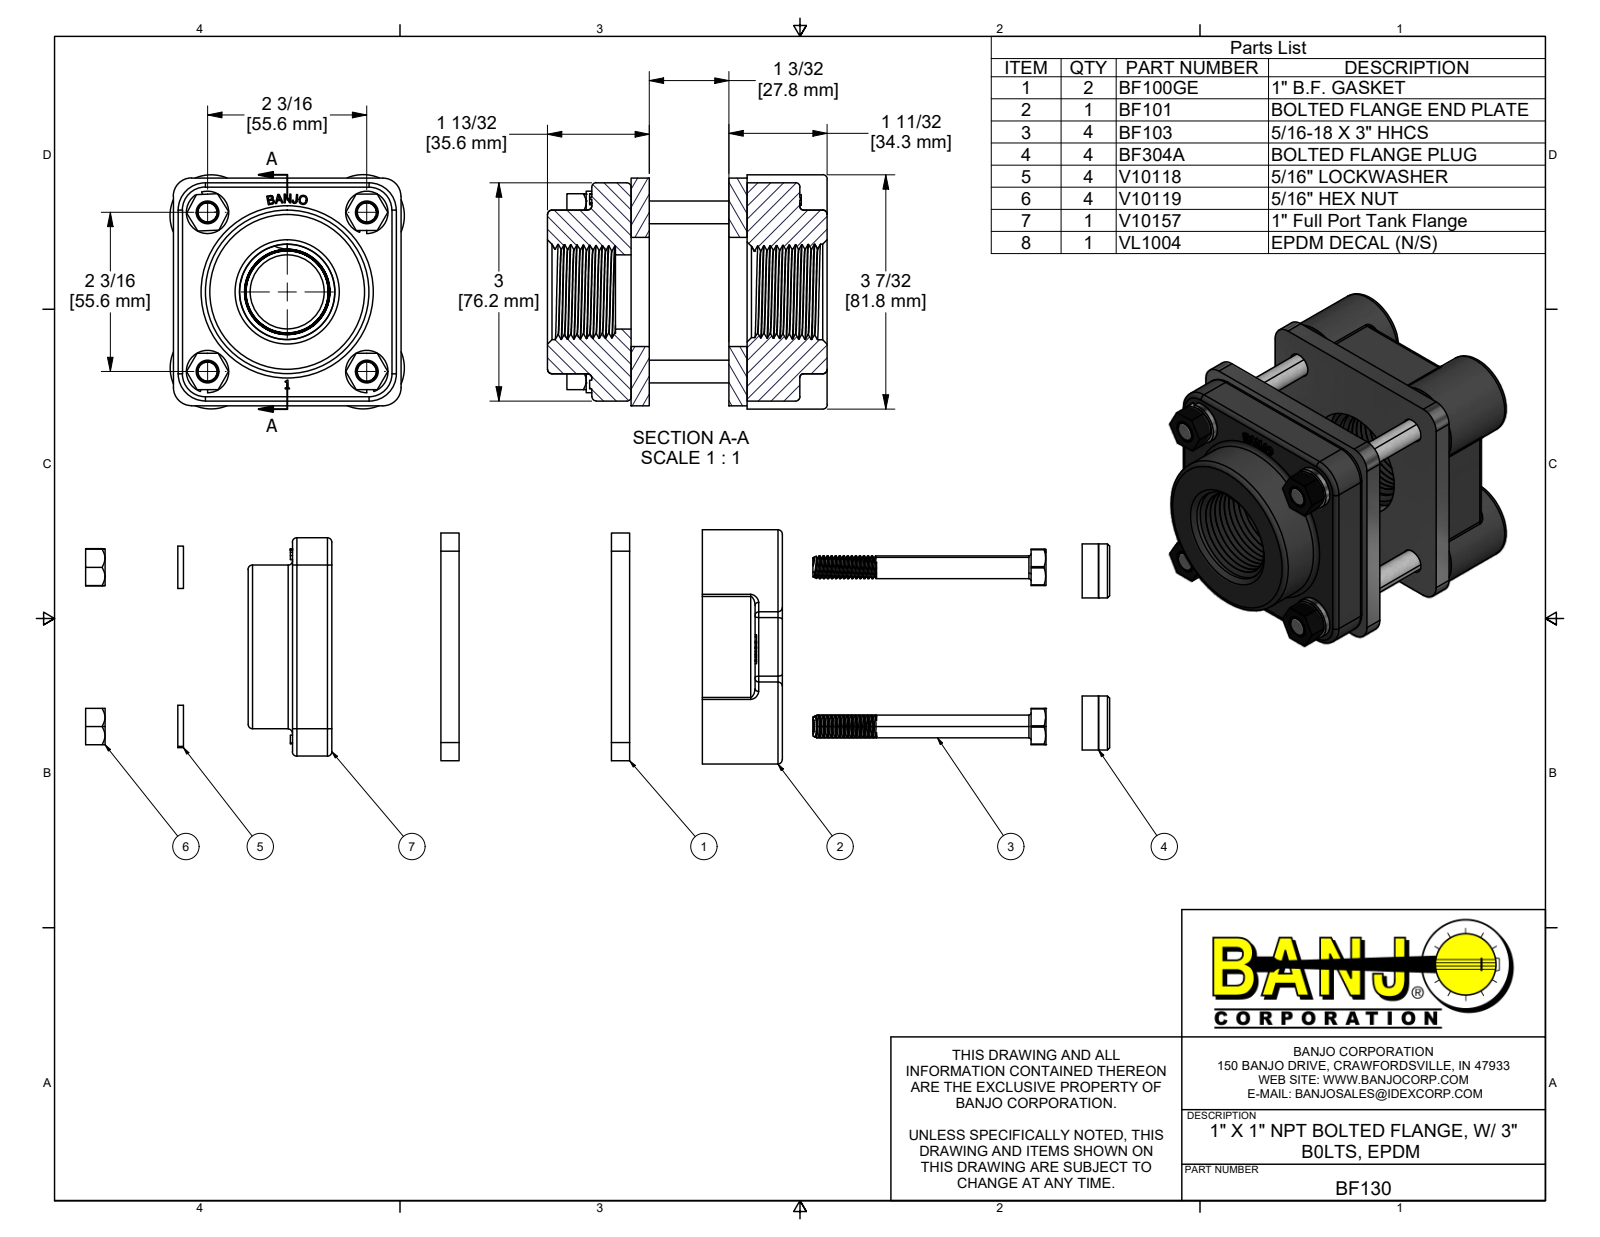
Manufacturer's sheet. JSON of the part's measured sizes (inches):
{"part_name": "BF130; BF101; BF103; BF304A (+4 more)", "step_written_by": "Autodesk Inventor 2019 (AUTOMOTIVE_DESIGN)", "units": "inches", "bodies": {"solids": 20, "faces": 1566, "planar": 486, "cylindrical": 448, "other": 632}, "overall_size": [21.039, 3.22, 3.22], "volume_in3": 18.68, "surface_area_in2": 231.9, "round_holes": [[0.252, 4], [0.322, 4], [0.34, 4], [0.344, 4], [0.35, 4], [0.72, 4], [0.745, 4], [1.02, 1], [1.5, 1]], "round_bosses_or_shafts": [[0.268, 60], [0.742, 4], [0.583, 4], [0.313, 4], [2.25, 1]], "partial_cylinders_radius": [[0.06, 20], [0.05, 8], [0.134, 8], [0.25, 4], [0.284, 4], [0.375, 4], [0.565, 4], [0.375, 1]], "face_to_face_distances": [0.25, 1.345, 1.595, 1.095, 0.065, 3.065, 2.445, 1.1, 3.235, 1.35], "hole_center_spacings": [2.139, 2.146, 2.194, 0.07, 0.078, 1.478, 1.547, 1.556]}
